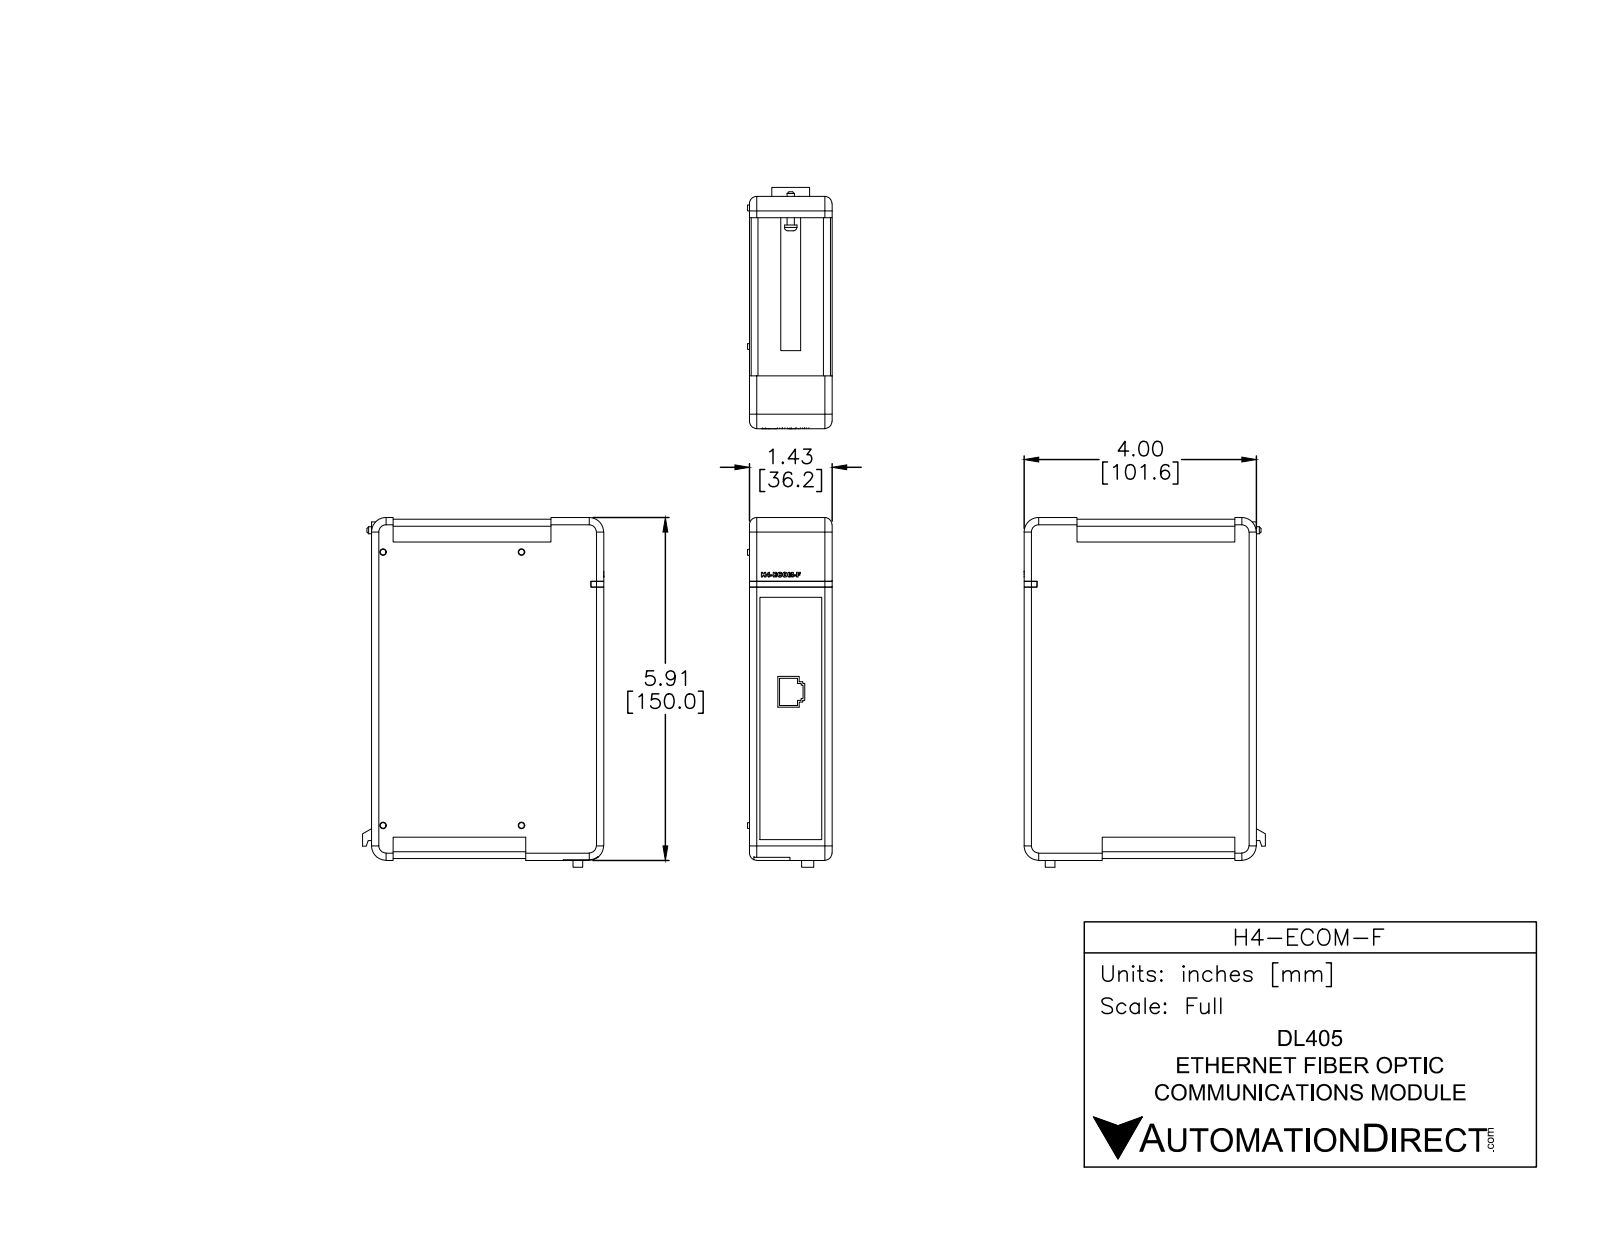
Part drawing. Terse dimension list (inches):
name: H4-ECOM-F
written by: SolidWorks 2014 (AUTOMOTIVE_DESIGN)
unit: in
bodies: 2 solids, 277 faces (201 planar, 34 cylindrical, 42 other)
size: 6.025 × 4.156 × 1.455
volume: 32.09 in³; area: 81.26 in²
bosses: 1× ⌀0.212, 1× ⌀0.123
rounds: 8× R0.125, 4× R0.12, 4× R0.25, 1× R0.145, 1× R0.171
face distances: 1.425, 0.03, 3.97, 1.395, 5.845, 5.875, 4, 0.2, 3.77, 3.8
